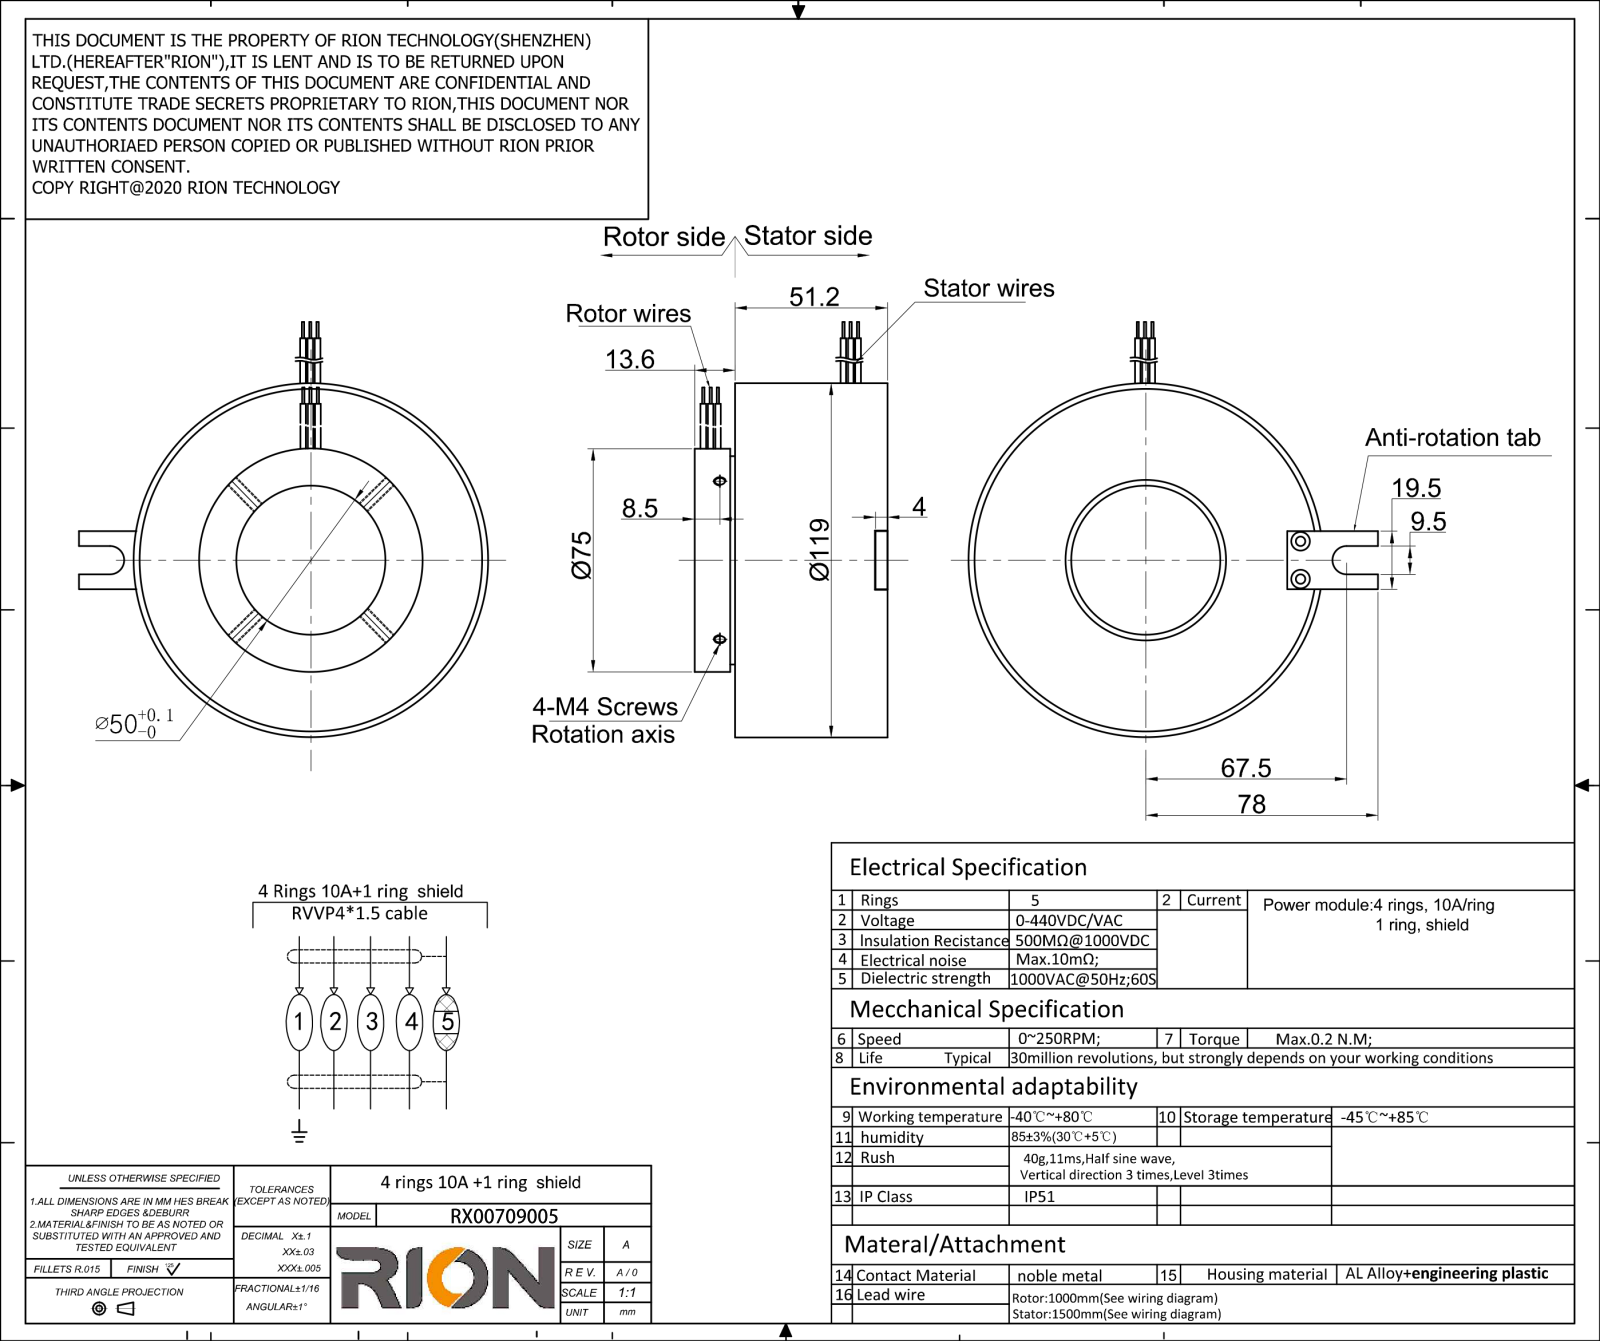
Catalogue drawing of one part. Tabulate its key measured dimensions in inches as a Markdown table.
| quantity | value |
| --- | --- |
| part name | MT150119-P1510-00(AC0023) |
| STEP written by | SolidWorks 2014 (CONFIG_CONTROL_DESIGN) |
| units | inches |
| bodies | 2 solids, 59 faces (25 planar, 26 cylindrical, 8 other) |
| overall size | 5.472 × 5.413 × 2.551 |
| volume | 30.73 in³ |
| surface area | 84.85 in² |
| round holes (diameter × count) | 0.13 × 4, 0.126 × 2, 1.969 × 1 |
| round bosses / shafts (diameter × count) | 0.315 × 2, 4.685 × 1, 2.953 × 1, 2.756 × 1 |
| partial cylindrical surfaces (radius × count) | 0.187 × 1, 0.197 × 1 |
| main face-to-face distances | 2.016, 0.535, 2.551, 0.472, 0.063, 2.079, 2.394, 1.921, 1.858, 0.157 |
| hole center spacings | 2.063, 0.5 |
